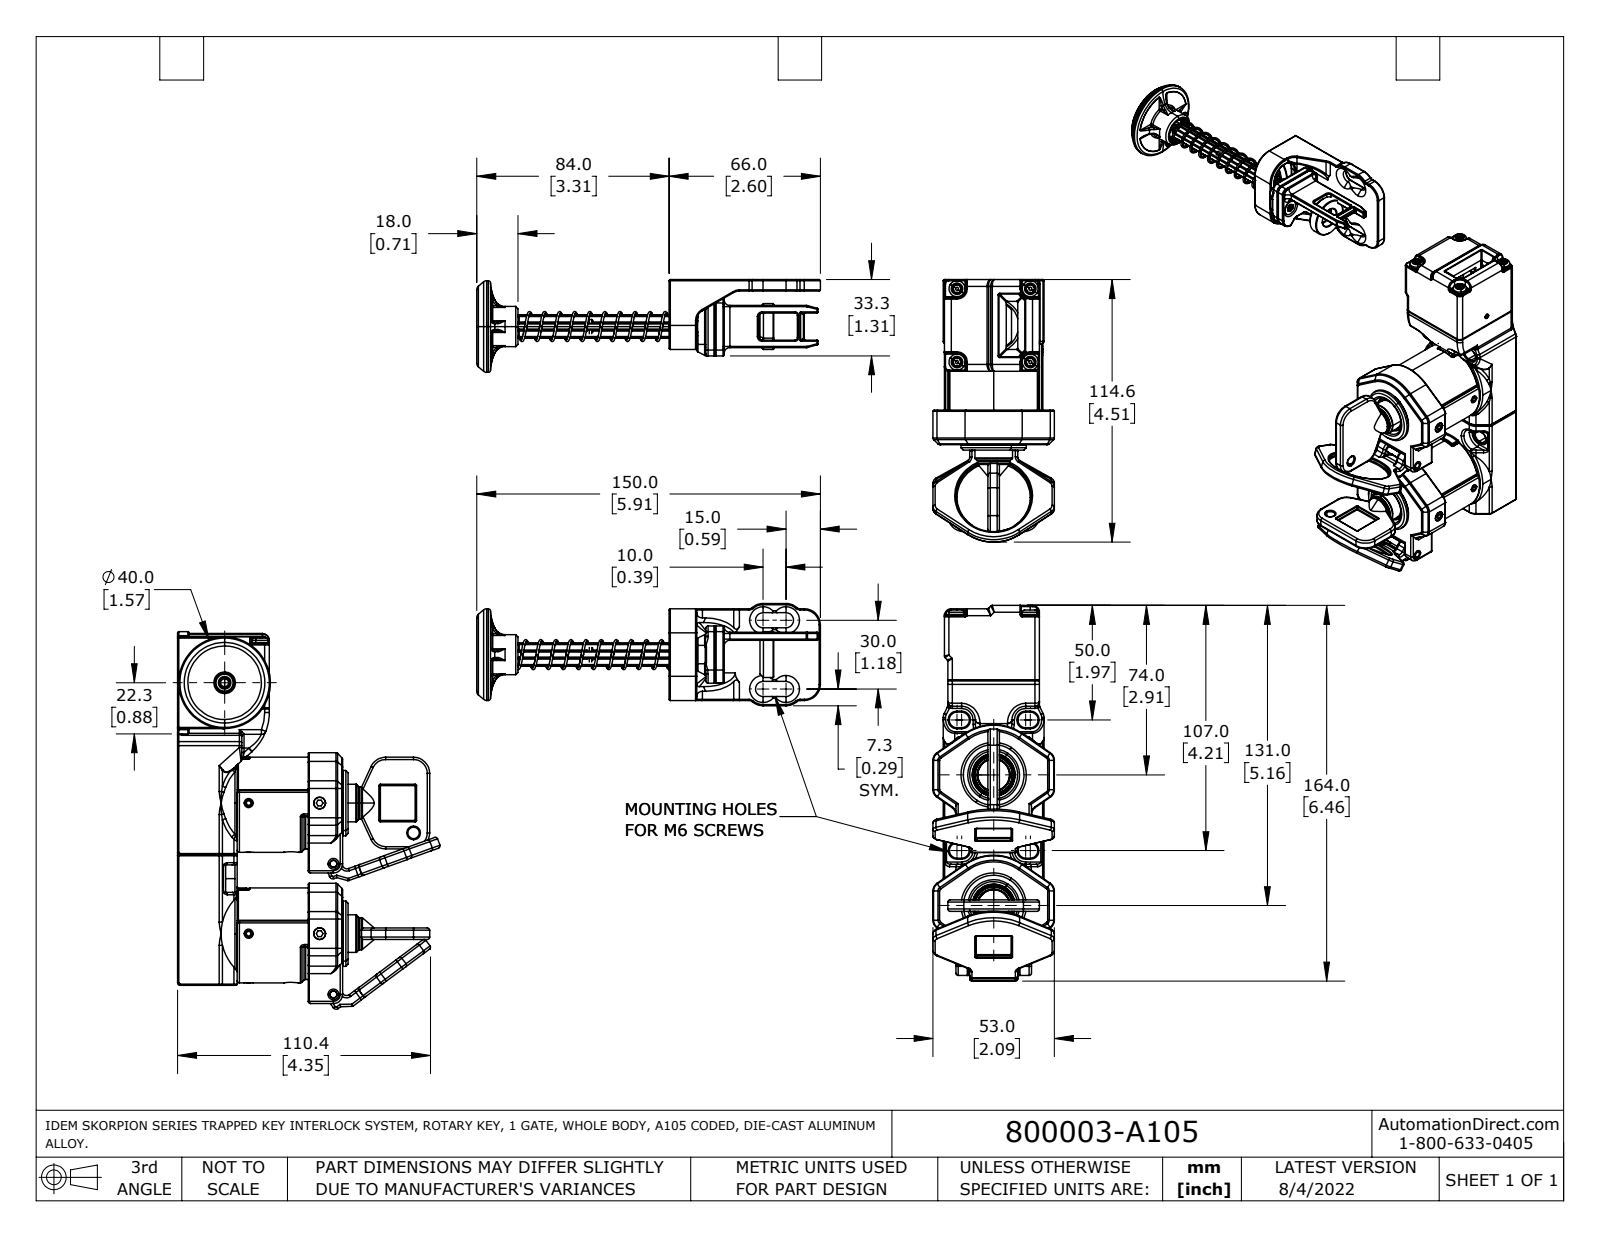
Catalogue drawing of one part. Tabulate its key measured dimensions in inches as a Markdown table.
| quantity | value |
| --- | --- |
| part name | 800003-A103_2; 800003-A103_1; 800003-A103 |
| STEP written by | SolidWorks 2021 (AUTOMOTIVE_DESIGN) |
| units | inches |
| bodies | 5 solids, 4585 faces (993 planar, 1815 cylindrical, 1777 other) |
| overall size | 9.397 × 6.487 × 4.346 |
| volume | 17.85 in³ |
| surface area | 213.7 in² |
| round holes (diameter × count) | 0.177 × 8, 0.138 × 7, 0.13 × 6, 0.157 × 6, 0.165 × 6, 0.315 × 4, 0.197 × 3, 0.087 × 2, 0.098 × 2, 0.12 × 2, 0.209 × 2, 0.728 × 2 |
| round bosses / shafts (diameter × count) | 0.051 × 10, 0.138 × 6, 0.291 × 4, 0.276 × 4, 0.154 × 4, 0.118 × 4, 1.575 × 3, 0.394 × 3 |
| partial cylindrical surfaces (radius × count) | 0.02 × 589, 0.039 × 267, 0.012 × 52, 0.079 × 41, 0.157 × 23, 0.031 × 18, 0.118 × 16, 0.059 × 12 |
| main face-to-face distances | 0.197, 2.244, 0.118, 0.079, 1.654, 0.157, 1.575, 2.047, 0.669, 1.535 |
| hole center spacings | 2.244, 0.822, 0.891, 1.26, 1.398, 0.28, 0.66, 0.704 |
